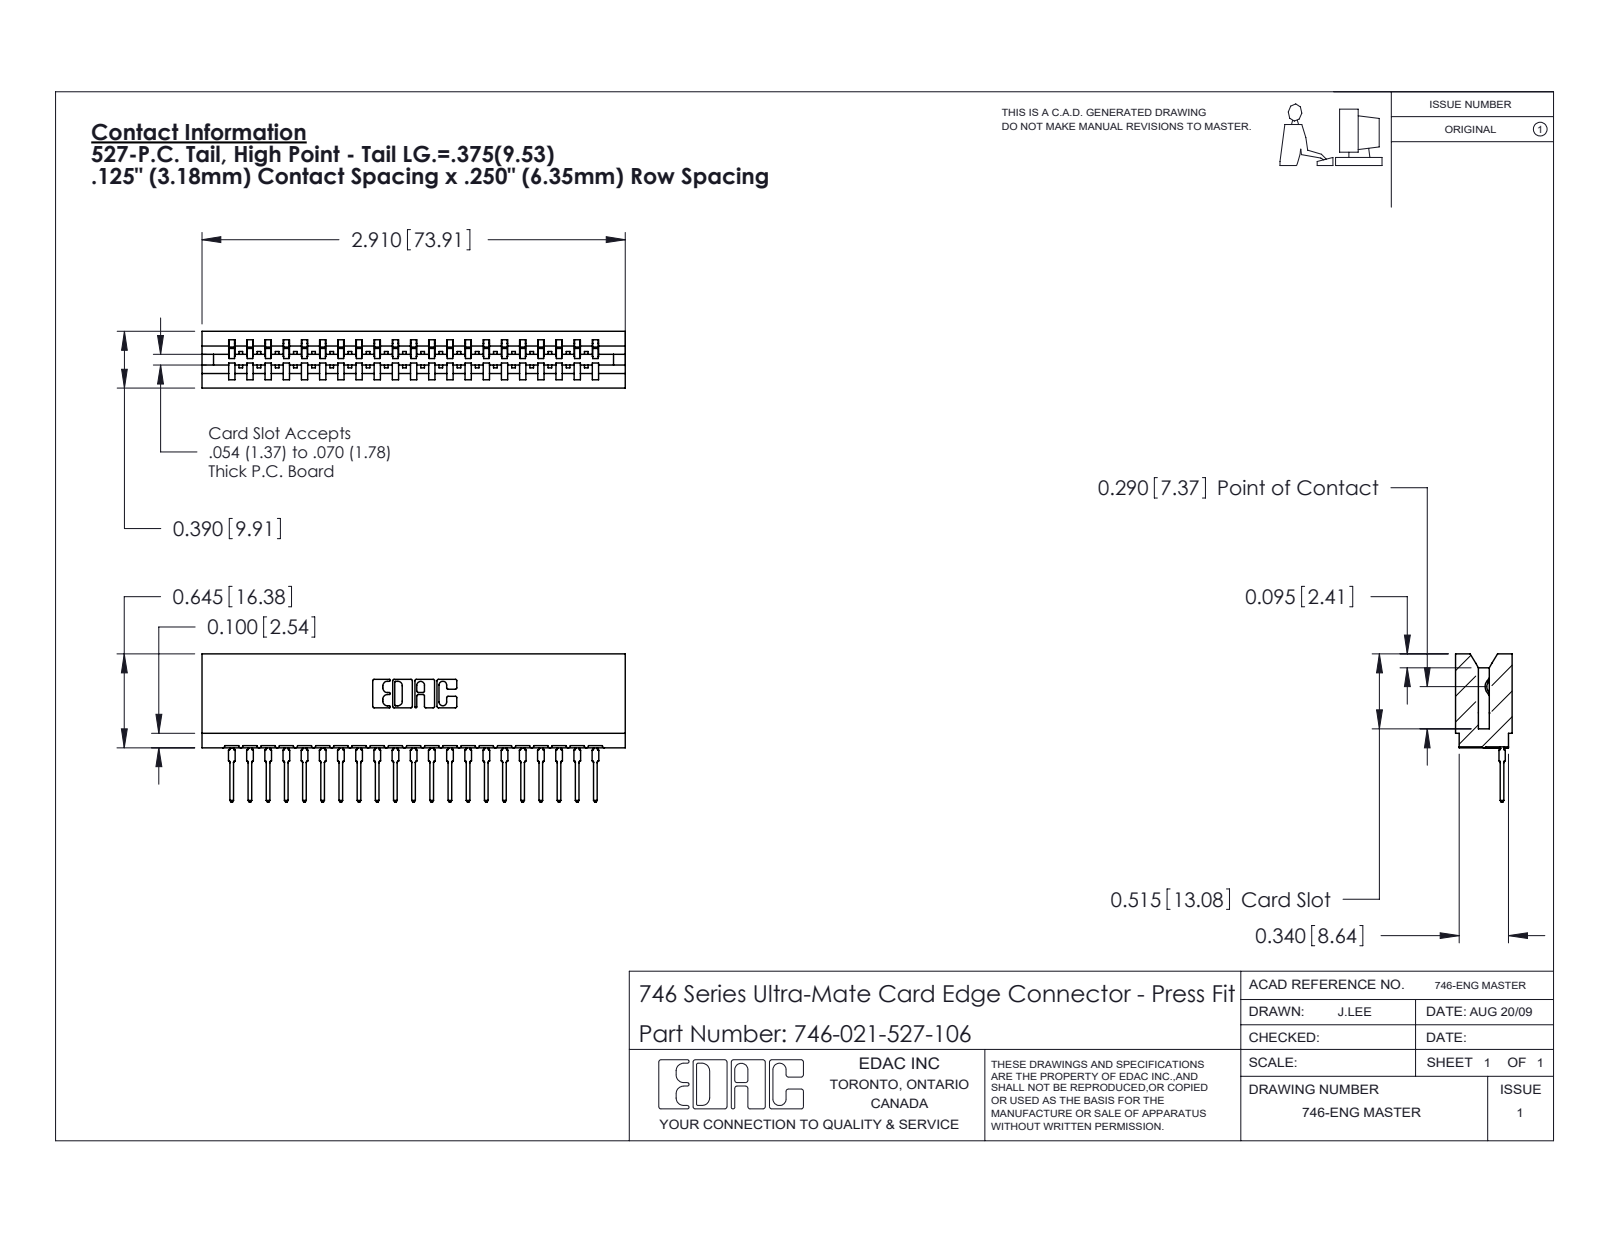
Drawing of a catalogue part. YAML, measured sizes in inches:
part_name: "746 Part_.515 Slot Depth - 06; 746-292-001_527; 746-021-527-106"
step_written_by: "SolidWorks 2020 (CONFIG_CONTROL_DESIGN)"
units: inches
bodies: {solids: 22, faces: 2366, planar: 1379, cylindrical: 441, other: 546}
overall_size: [2.91, 1.019, 0.39]
volume: 0.48
surface_area: 17.73
partial_cylinders:
  - {radius: 0.021, count: 42}
  - {radius: 0.01, count: 22}
  - {radius: 0.015, count: 22}
  - {radius: 0.007, count: 6}
  - {radius: 0.031, count: 6}
  - {radius: 0.005, count: 4}
  - {radius: 0.011, count: 4}
  - {radius: 0.026, count: 3}
face_to_face_distances: [0.057, 0.333, 0.25, 0.39, 0.5, 0.025, 0.307, 0.042, 0.083, 0.125]
